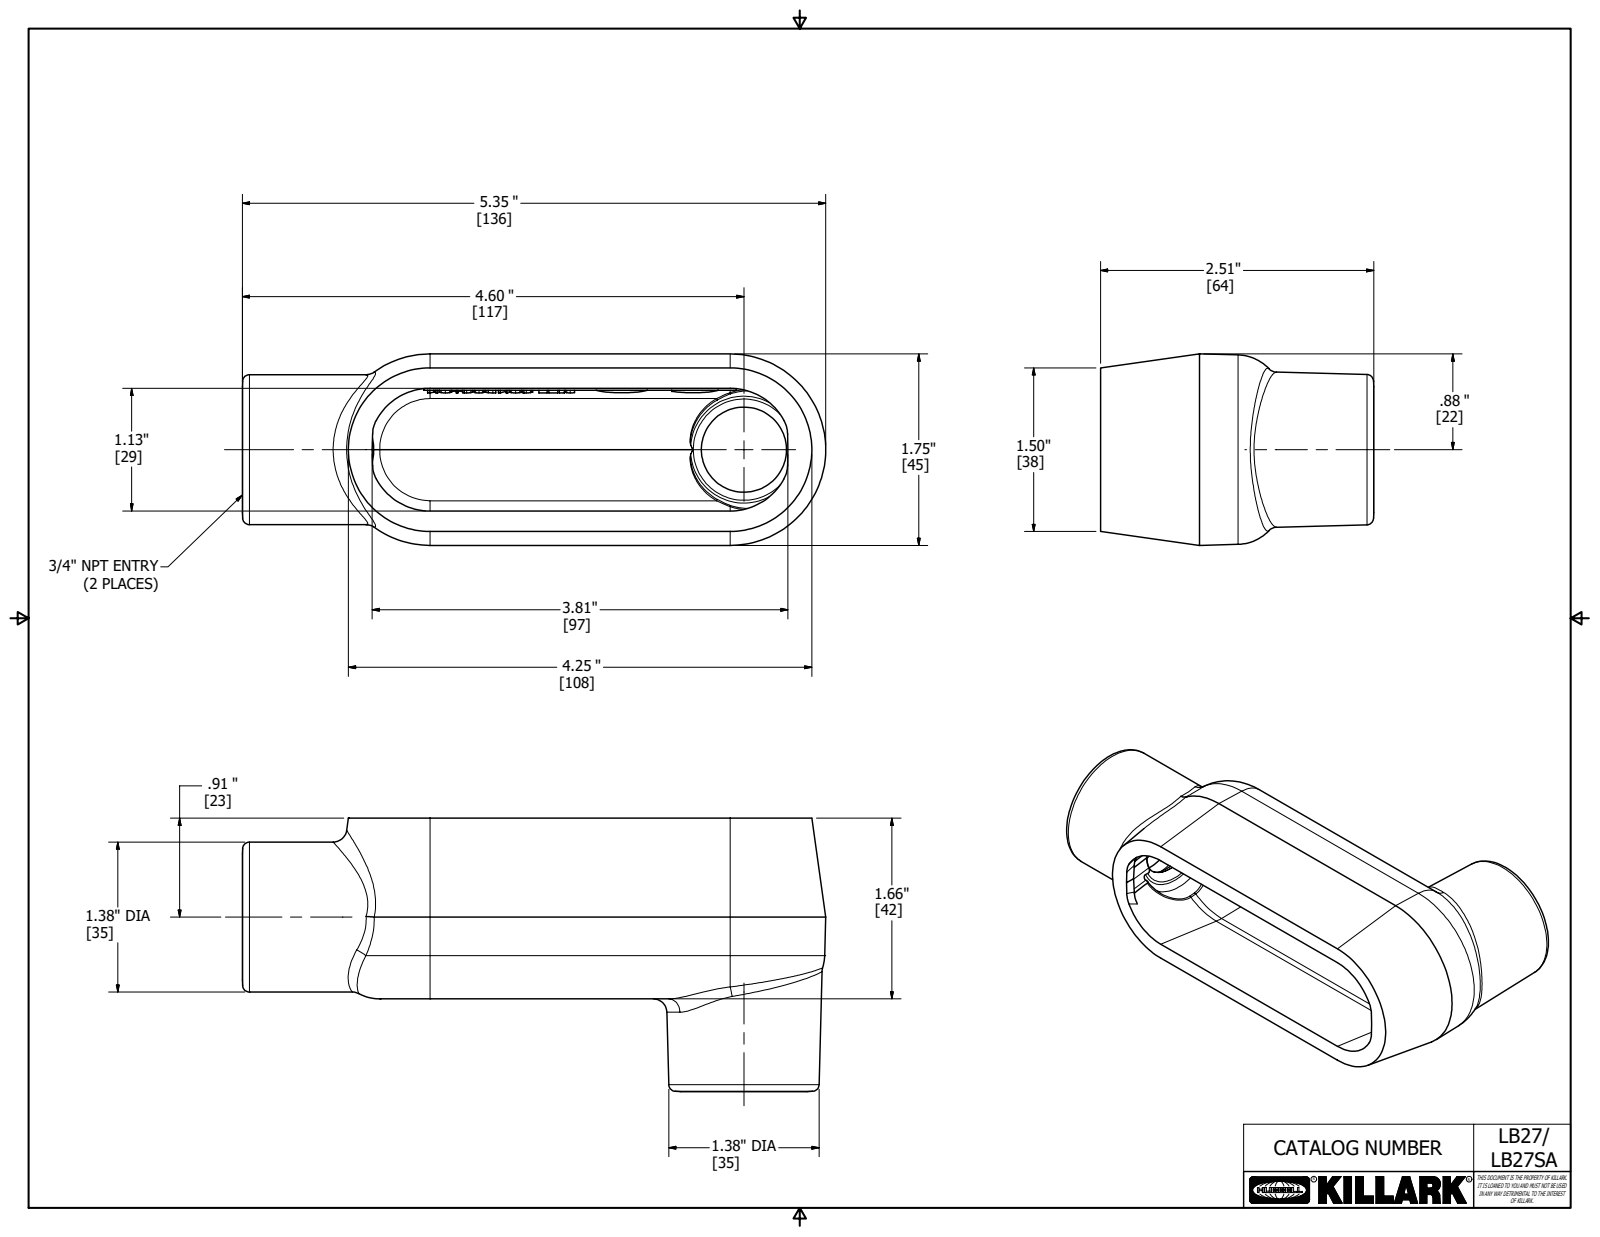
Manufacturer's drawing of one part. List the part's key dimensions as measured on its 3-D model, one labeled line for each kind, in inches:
Part name (STEP PRODUCT): 17655-2
STEP written by: Autodesk Inventor 2018 (AUTOMOTIVE_DESIGN)
Units: inches
Bodies: 1 solid, 858 faces (511 planar, 38 cylindrical, 309 other)
Overall size (bounding box): 5.349 × 2.506 × 1.755
Volume: 5.116 in³ · Surface area: 57.12 in²
Round holes (diameter × count): ⌀1.055 ×2, ⌀0.047 ×1, ⌀0.407 ×1, ⌀1.109 ×1
Round bosses / shafts (diameter × count): ⌀1.375 ×1, ⌀0.5 ×1, ⌀0.056 ×1
Partial cylindrical surfaces — rounded edges, fillets, slot ends (radius × count): R0.062 ×6, R0.125 ×4, R0.219 ×2, R0.406 ×2, R0.5 ×2, R0.006 ×1, R0.009 ×1, R0.016 ×1
Main face-to-face distances: 0.186, 1.656, 0.187, 0.217, 0.031, 0.031, 1.625, 0.062, 0.248, 1.359
Hole centre spacings: 0.122
